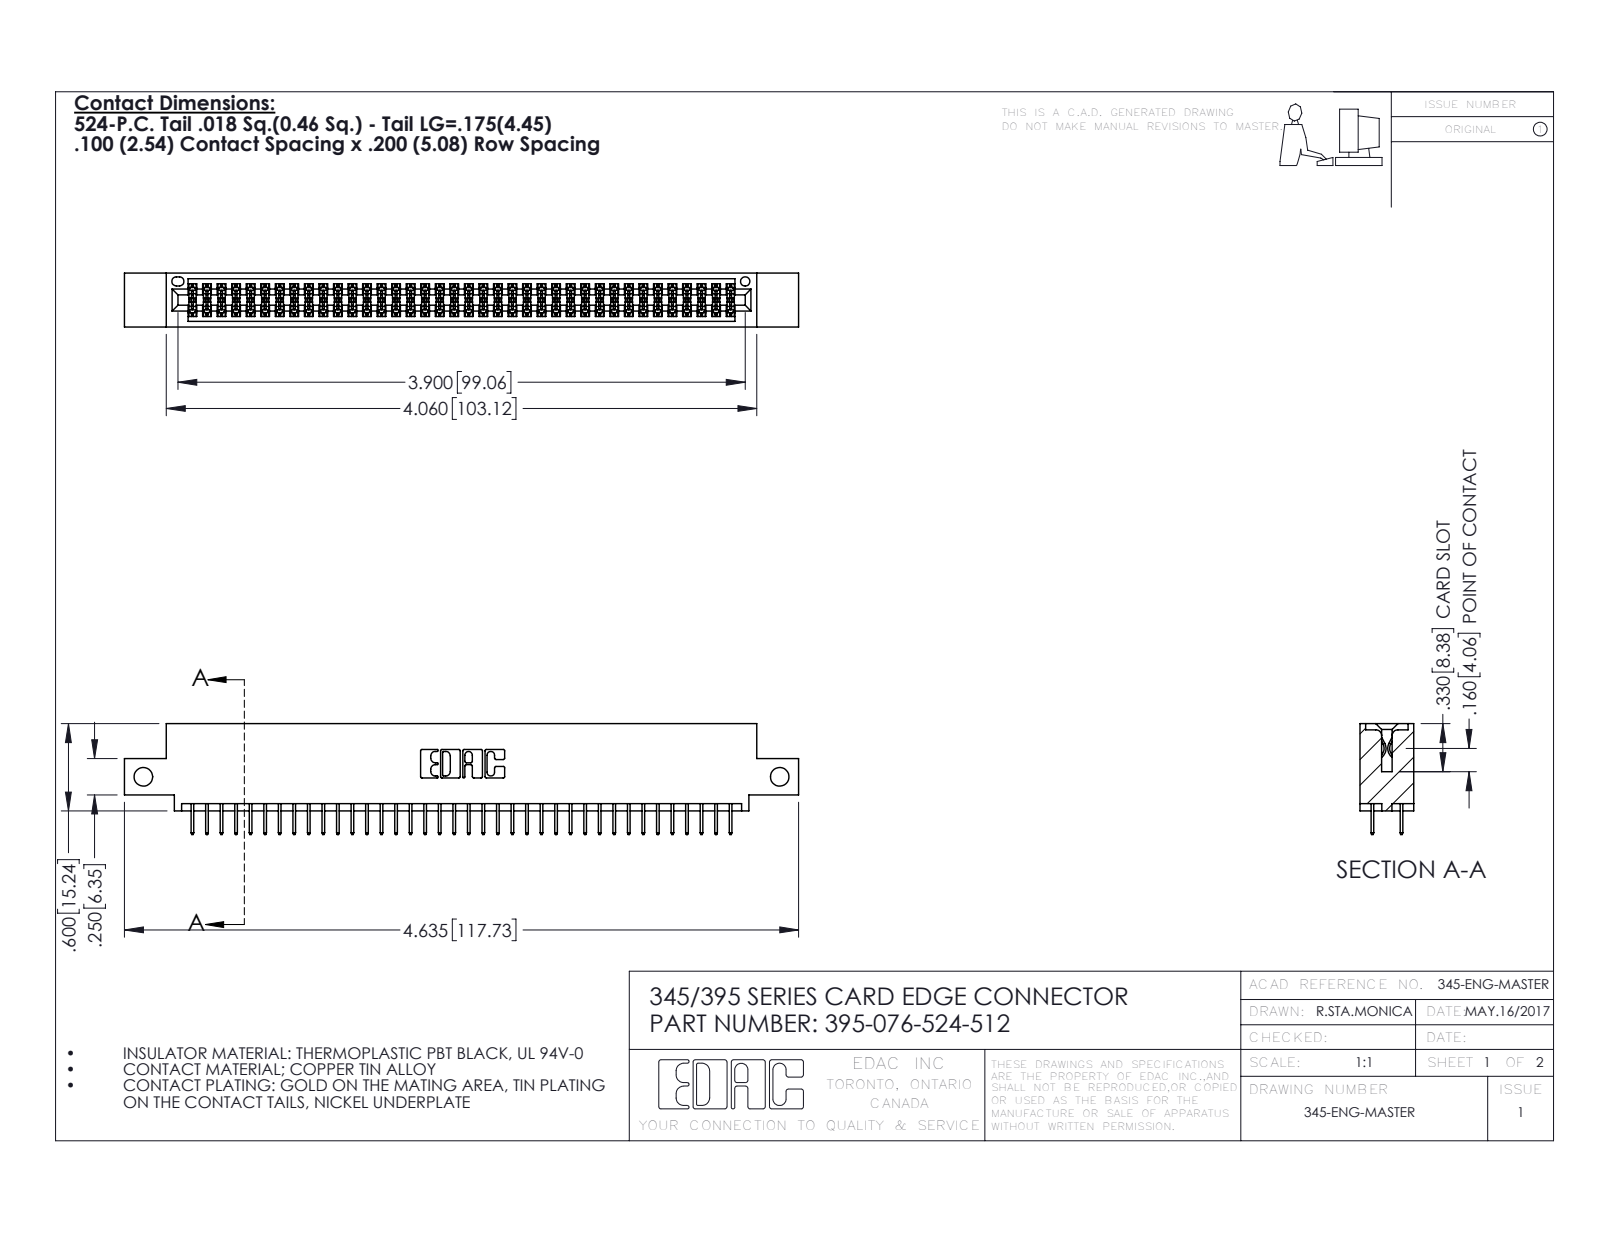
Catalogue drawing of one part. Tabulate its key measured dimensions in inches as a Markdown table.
| quantity | value |
| --- | --- |
| part name | 345-292-001_345-293-124; 345 Part_0.110 Offset - Side Mount; 395-076-524-512 |
| STEP written by | SolidWorks 2016 (CONFIG_CONTROL_DESIGN) |
| units | inches |
| bodies | 77 solids, 4234 faces (3048 planar, 1186 cylindrical, 0 other) |
| overall size | 4.635 × 0.762 × 0.37 |
| volume | 0.679 in³ |
| surface area | 24.83 in² |
| round holes (diameter × count) | 0.128 × 2, 0.064 × 1 |
| partial cylindrical surfaces (radius × count) | 0.006 × 114, 0.01 × 22, 0.007 × 6, 0.031 × 6, 0.026 × 3, 0.014 × 2, 0.019 × 2, 0.022 × 2 |
| main face-to-face distances | 0.072, 0.298, 0.2, 0.37, 0.098, 0.272, 0.025, 0.225, 0.072, 0.175 |
| hole center spacings | 4.375 |
